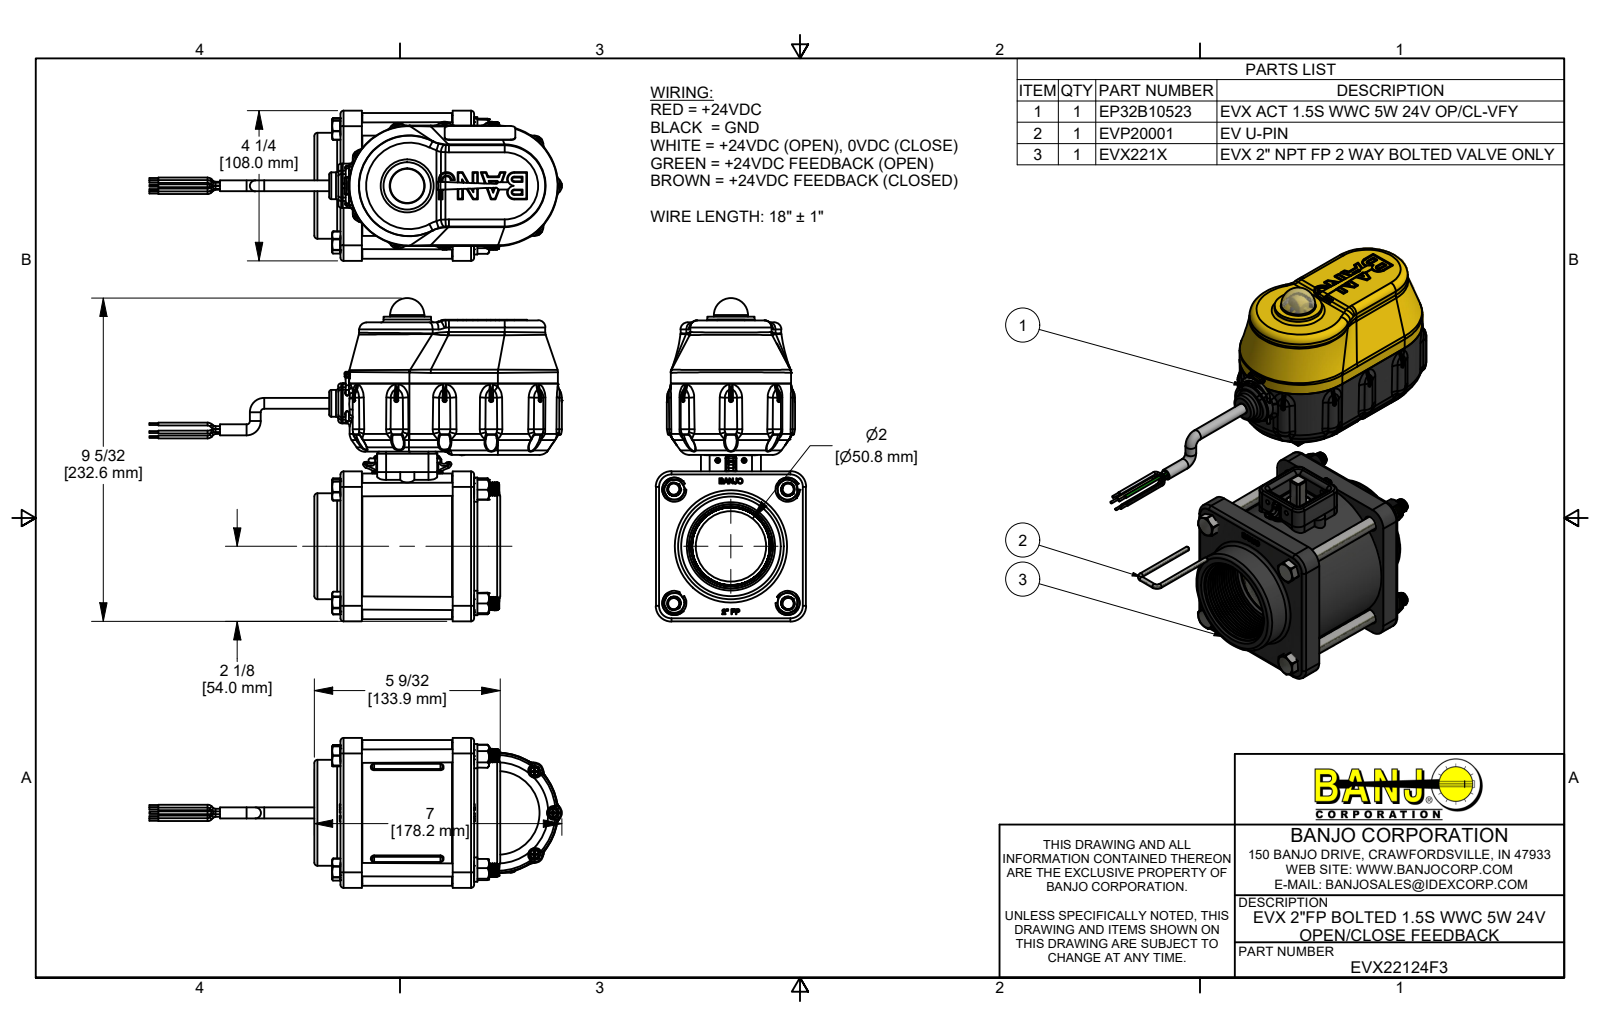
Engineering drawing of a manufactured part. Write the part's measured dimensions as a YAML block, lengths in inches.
part_name: "EVX22124F3; EP32B10523; B61905PPHS; B632038PM (+8 more)"
step_written_by: "Autodesk Inventor 2021 (AUTOMOTIVE_DESIGN)"
units: inches
bodies: {solids: 96, faces: 11574, planar: 2992, cylindrical: 3391, other: 5191}
overall_size: [11.685, 9.157, 4.25]
volume: 70.85
surface_area: 752
round_holes:
  - {diameter: 0.095, count: 11}
  - {diameter: 0.15, count: 11}
  - {diameter: 0.08, count: 7}
  - {diameter: 0.107, count: 4}
  - {diameter: 0.126, count: 4}
  - {diameter: 0.136, count: 4}
  - {diameter: 0.148, count: 4}
  - {diameter: 0.15, count: 4}
  - {diameter: 0.17, count: 4}
  - {diameter: 0.307, count: 4}
  - {diameter: 0.375, count: 4}
  - {diameter: 0.385, count: 4}
round_bosses_or_shafts:
  - {diameter: 0.324, count: 60}
  - {diameter: 0.08, count: 25}
  - {diameter: 0.25, count: 17}
  - {diameter: 0.14, count: 11}
  - {diameter: 0.108, count: 11}
  - {diameter: 0.085, count: 11}
  - {diameter: 0.058, count: 10}
  - {diameter: 0.375, count: 5}
partial_cylinders:
  - {radius: 0.013, count: 180}
  - {radius: 0.04, count: 145}
  - {radius: 0.02, count: 98}
  - {radius: 0.01, count: 94}
  - {radius: 0.005, count: 57}
  - {radius: 0.03, count: 47}
  - {radius: 0.015, count: 33}
  - {radius: 0.08, count: 28}
face_to_face_distances: [0.1, 2.565, 0.61, 3.18, 0.695, 3.095, 0.085, 2.485, 3.79, 0.06]
hole_center_spacings: [1.513, 2.849, 3.789, 0.487, 0.668, 1.226, 1.282, 1.283]
